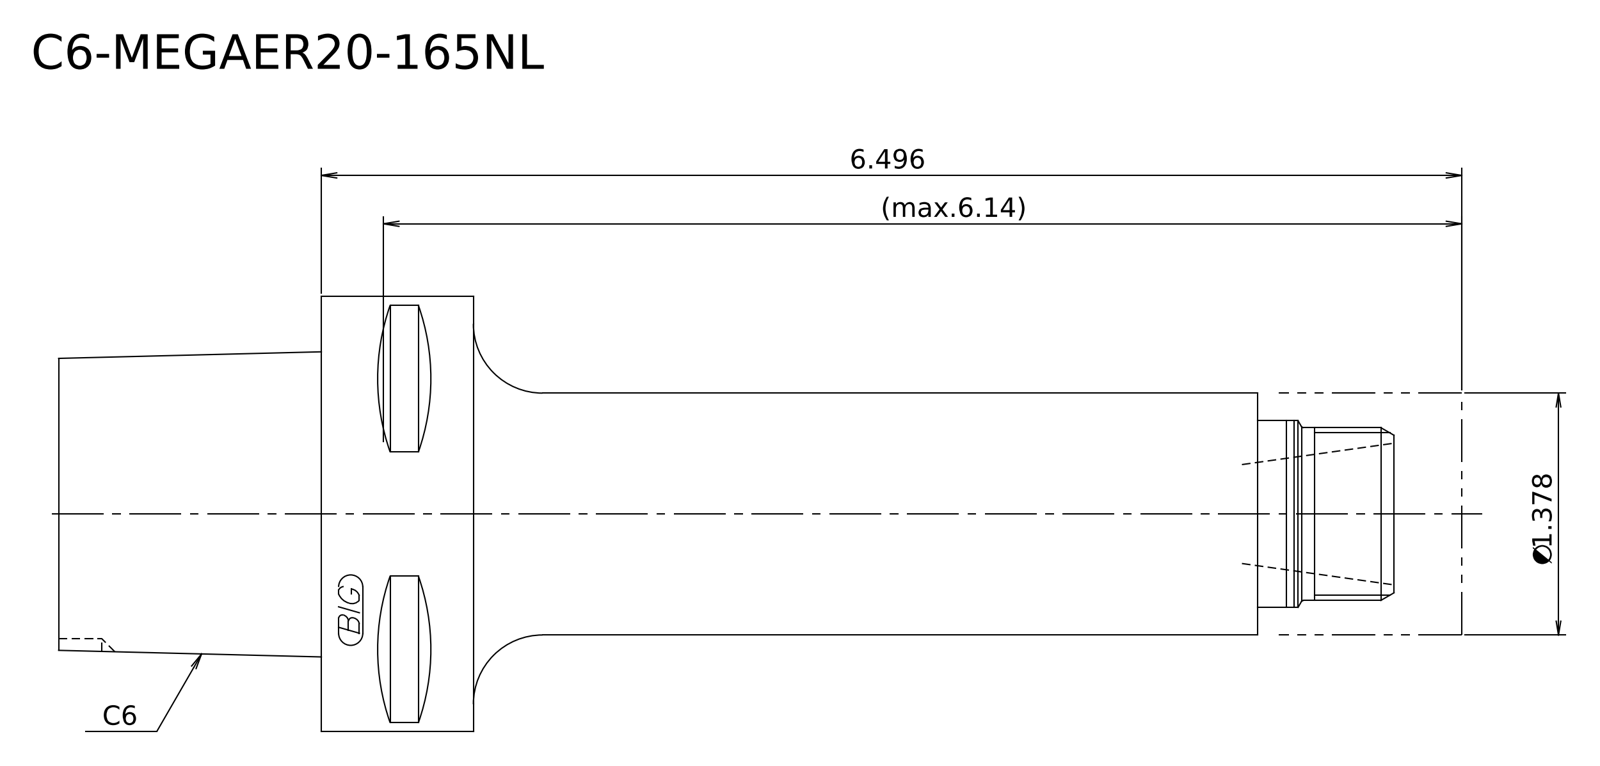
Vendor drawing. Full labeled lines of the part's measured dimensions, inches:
STEP written by: Kubotek KeyCreator 2011 V10.0.2 (22737) (automotive_design)
Units: inches
Bodies: 2 solids, 18 faces (7 planar, 5 cylindrical, 6 other)
Overall size (bounding box): 7.992 × 2.48 × 2.48
Volume: 16.76 in³ · Surface area: 52.55 in²
Round bosses / shafts (diameter × count): ⌀2.48 ×1, ⌀1.378 ×1, ⌀1.063 ×1, ⌀0.984 ×1
Main face-to-face distances: 1.496, 5.453, 6.949, 1.043, 6.496, 7.992, 5.63, 4.587, 0.866, 2.362
